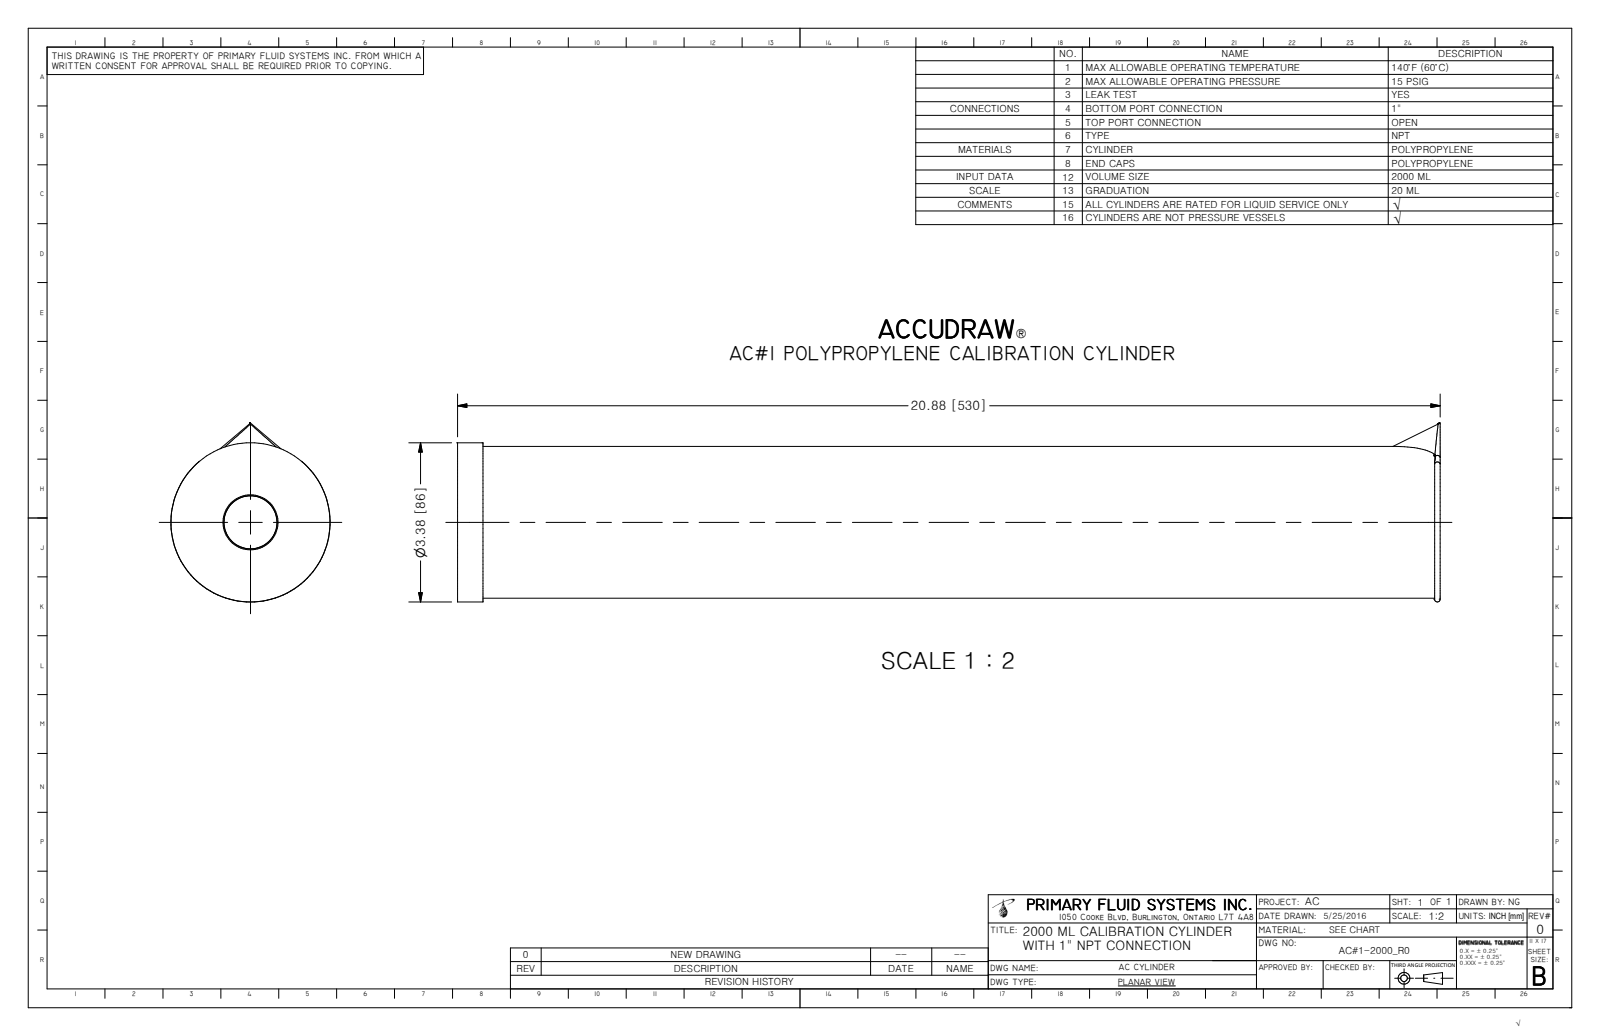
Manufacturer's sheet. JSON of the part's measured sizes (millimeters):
{"part_name": "AC#1-2000_R0; AC-2B-2000; AC#1-2000-TUBE", "step_written_by": "Autodesk Inventor 2009 (AUTOMOTIVE_DESIGN)", "units": "millimeters", "bodies": {"solids": 2, "faces": 24, "planar": 10, "cylindrical": 4, "other": 10}, "overall_size": [530.4, 96.5, 85.9], "volume_mm3": 448400, "surface_area_mm2": 276200, "round_holes": [[76.4, 1]], "round_bosses_or_shafts": [[85.9, 1], [81.9, 1], [74.9, 1]], "face_to_face_distances": [19.1, 13.7, 5.3, 530.4, 516.6, 511.3, 527.4, 513.6, 508.3, 3]}
